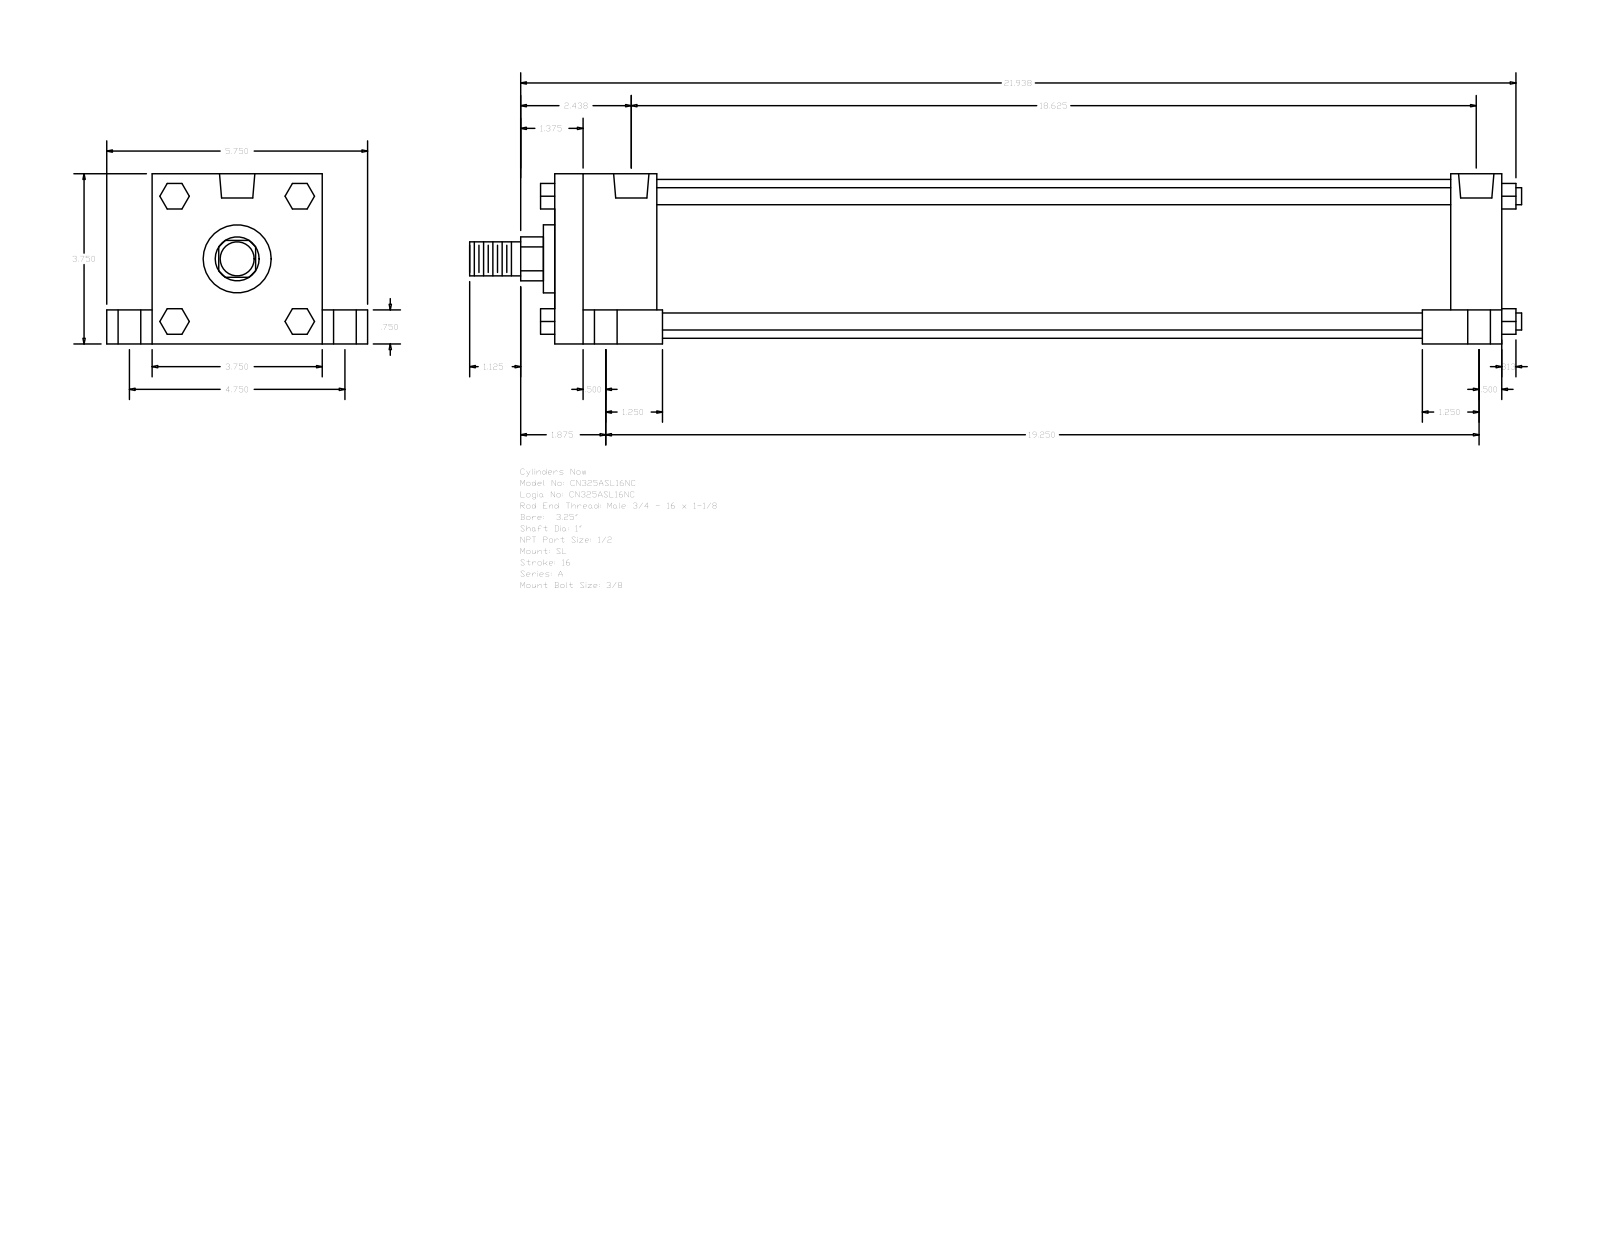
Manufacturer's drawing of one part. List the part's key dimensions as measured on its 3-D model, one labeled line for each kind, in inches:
Part name (STEP PRODUCT): A_SL__0325_1
STEP written by: GSSL Pune (CONFIG_CONTROL_DESIGN)
Units: inches
Bodies: 0 solids, 150 faces (114 planar, 36 cylindrical, 0 other)
Overall size (bounding box): 23.187 × 5.75 × 3.75
Round holes (diameter × count): ⌀0.344 ×4, ⌀0.5 ×4, ⌀0.75 ×4, ⌀0.778 ×2
Round bosses / shafts (diameter × count): ⌀0.375 ×4, ⌀3.5 ×1, ⌀1.5 ×1, ⌀1 ×1, ⌀0.75 ×1
Partial cylindrical surfaces — rounded edges, fillets, slot ends (radius × count): R0.484 ×1
Main face-to-face distances: 3.75, 20.875, 0.75, 1, 4.75, 3, 1.125, 2.25, 19.75, 17.5
Hole centre spacings: 0.125, 2.376, 2.383, 2.441, 2.473, 4.75, 18.375, 18.5
